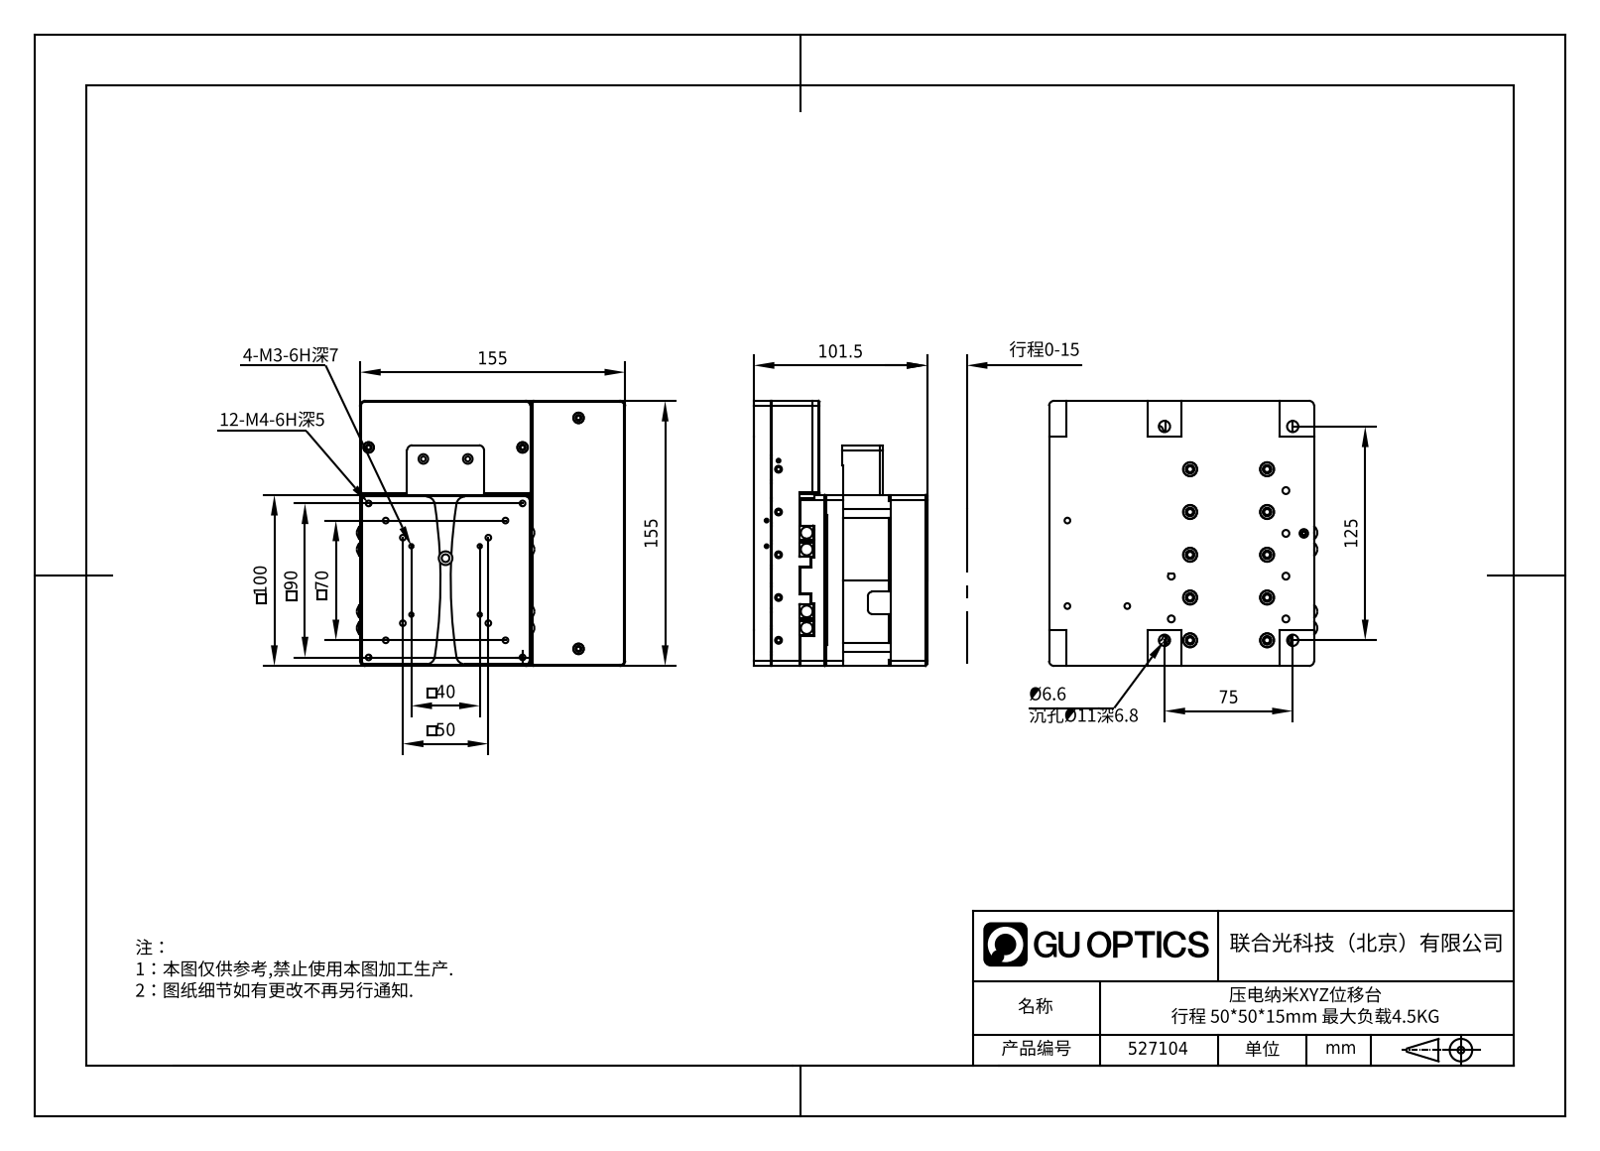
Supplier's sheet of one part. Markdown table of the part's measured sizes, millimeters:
| quantity | value |
| --- | --- |
| part name | 527104 |
| STEP written by | SolidWorks 2020 (CONFIG_CONTROL_DESIGN) |
| units | millimeters |
| bodies | 24 solids, 1881 faces (985 planar, 668 cylindrical, 228 other) |
| overall size | 156.9 × 155 × 101.5 |
| volume | 1 446 000 mm³ |
| surface area | 366 141 mm² |
| round holes (diameter × count) | 3.4 × 44, 2.5 × 41, 6 × 40, 3.3 × 32, 4.5 × 27, 8 × 27, 4 × 18, 1.6 × 6, 5 × 6, 2.9 × 4, 5.6 × 4, 6.2 × 4 |
| round bosses / shafts (diameter × count) | 3 × 62, 6.9 × 8, 40 × 1 |
| partial cylindrical surfaces (radius × count) | 2.5 × 85, 2 × 29, 3 × 26, 1 × 15, 5 × 13, 10 × 8, 0.5 × 6, 1.5 × 5 |
| main face-to-face distances | 8.5, 8, 0.5, 16.5, 24.5, 16, 1, 42.5, 3.5, 24 |
| hole center spacings | 25, 50, 16.65, 57.38, 75, 51.48, 39.08, 67.4 |
